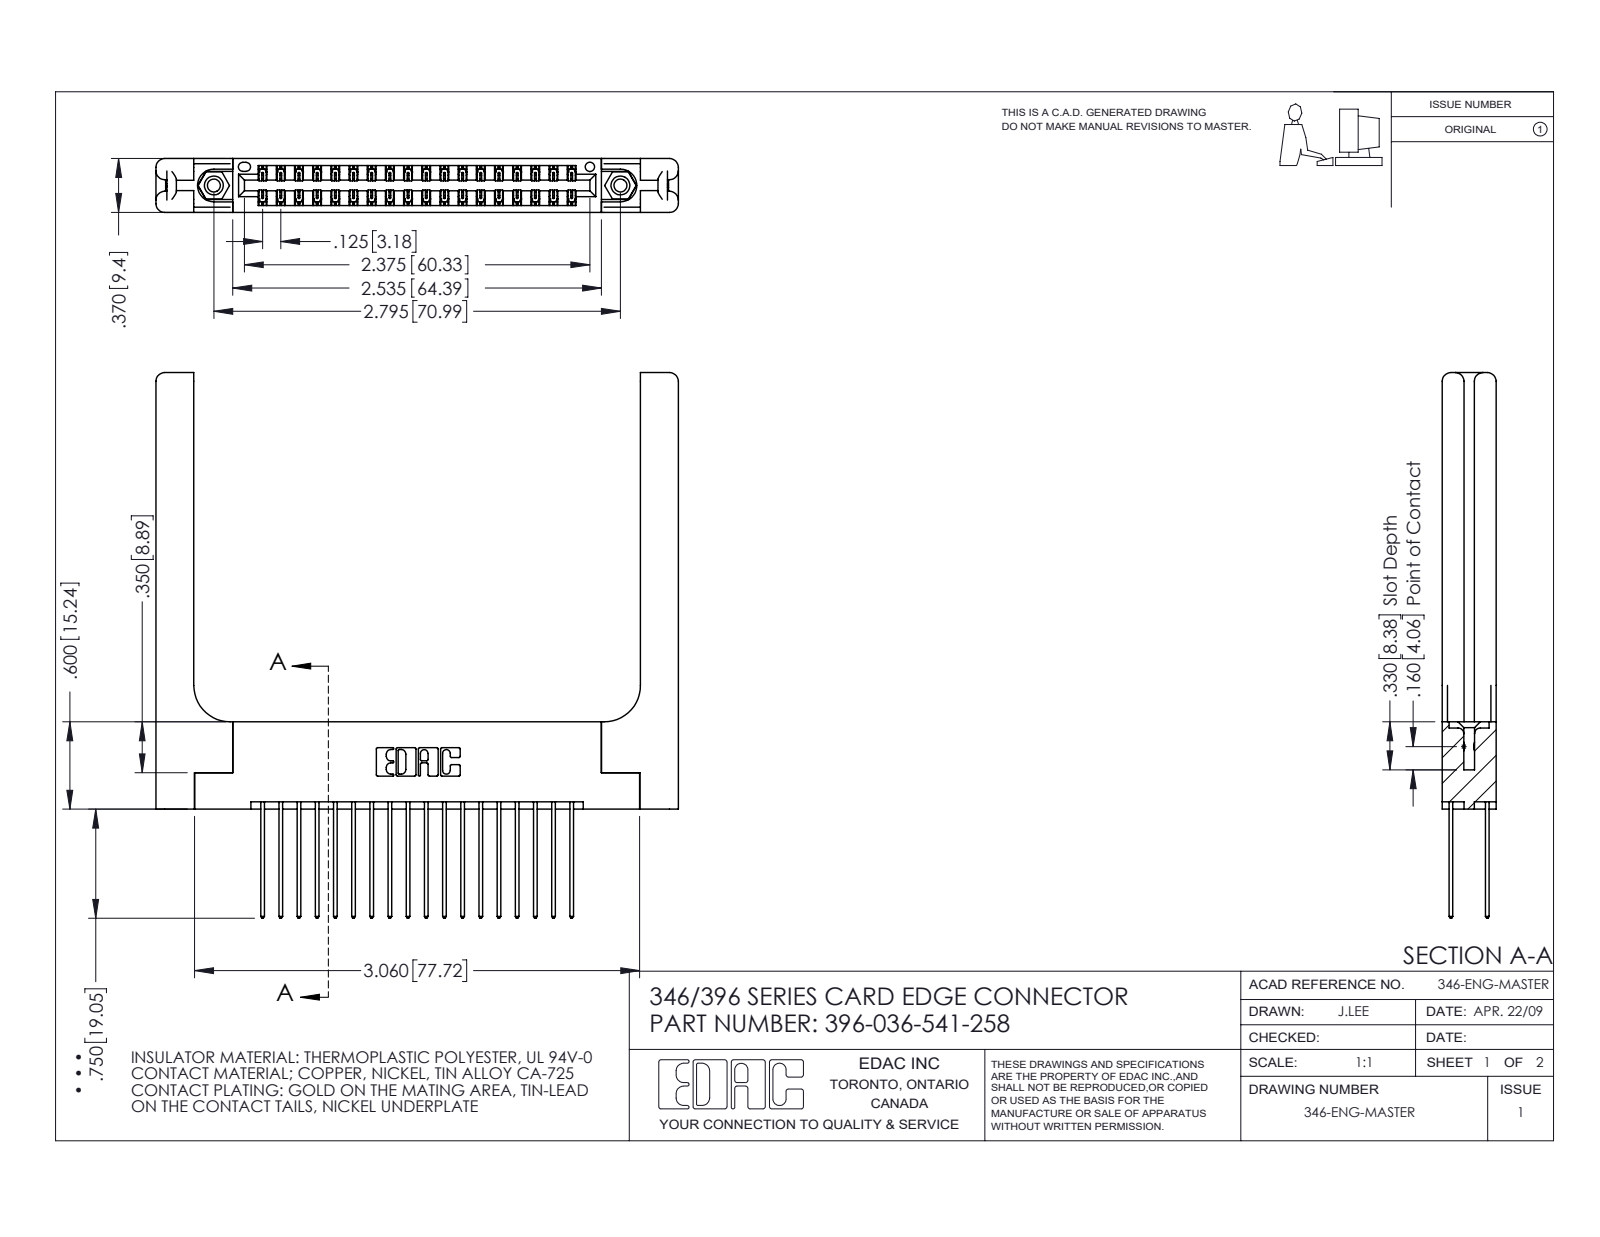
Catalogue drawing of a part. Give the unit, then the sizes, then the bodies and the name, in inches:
Units: inches
Overall size (bounding box): 3.75 × 3.591 × 0.37
Round holes (diameter × count): ⌀0.089 ×2, ⌀0.125 ×2, ⌀0.156 ×2, ⌀0.064 ×1
Round bosses / shafts (diameter × count): ⌀0.155 ×2
Partial cylindrical surfaces — rounded edges, fillets, slot ends (radius × count): R0.006 ×54, R0.01 ×36, R0.01 ×22, R0.06 ×16, R0.007 ×6, R0.031 ×6, R0.026 ×3, R0.014 ×2
Main face-to-face distances: 0.37, 0.072, 0.048, 0.322, 0.25, 0.148, 0.15, 0.025, 0.298, 0.275
Hole centre spacings: 0.246, 2.588, 2.795
Volume: 1.001 in³ · Surface area: 27.65 in²
Bodies: 41 solids, 2250 faces (1484 planar, 706 cylindrical, 60 other)
Part name (STEP PRODUCT): 396-036-541-258; 345-250-001_345-250-001-102; 346 Part_Flush Mounting Lugs - 0.156 Dia-TH; 345-292-001_345-293-141 (+1 more)
STEP written by: SolidWorks 2016 (CONFIG_CONTROL_DESIGN)
